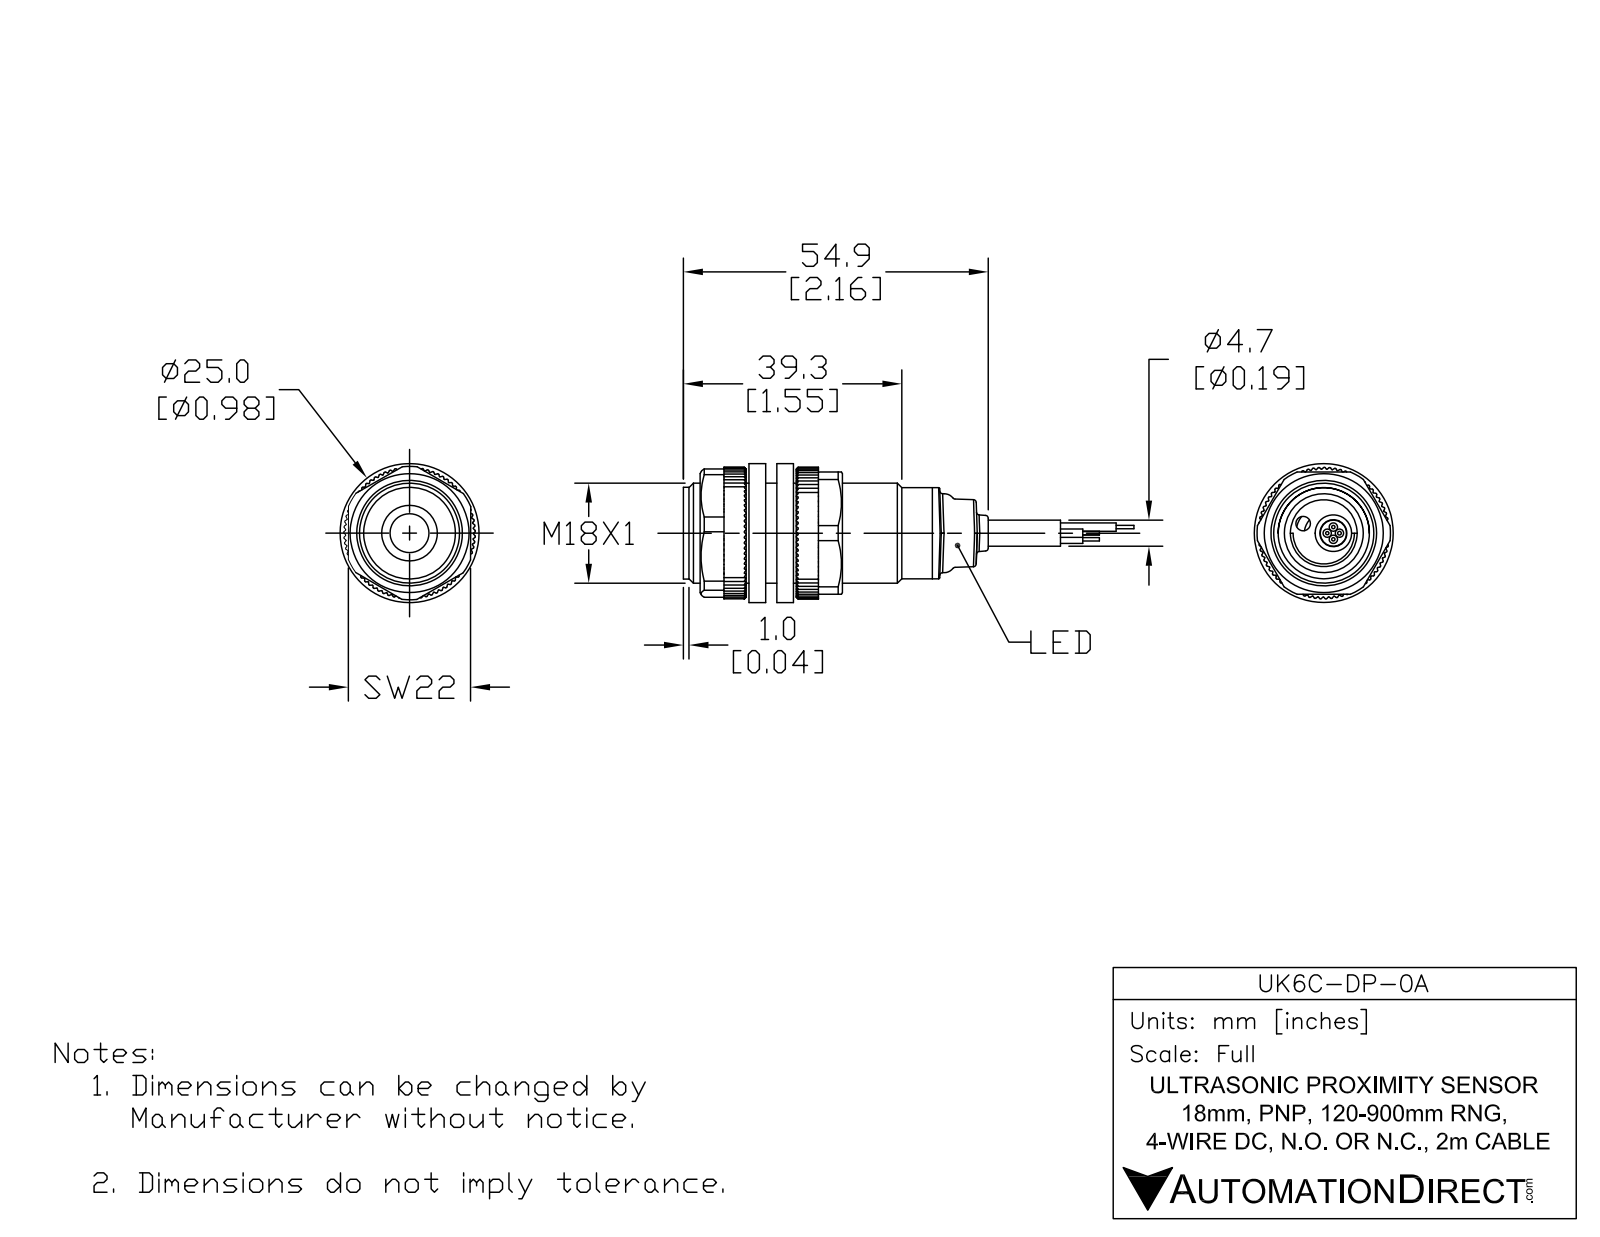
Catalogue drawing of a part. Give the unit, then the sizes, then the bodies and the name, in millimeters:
Units: millimetres
Overall size (bounding box): 89.8 × 18 × 18
Round holes (diameter × count): ⌀4.7 ×1, ⌀9.5 ×1
Round bosses / shafts (diameter × count): ⌀18 ×1, ⌀16.4 ×1, ⌀15.8 ×1, ⌀14.2 ×1
Partial cylindrical surfaces — rounded edges, fillets, slot ends (radius × count): R0.2 ×1, R0.5 ×1
Main face-to-face distances: 43.8, 1, 44.8, 1, 44.8, 49.9, 49.8, 48.8, 5.1, 6.5
Hole centre spacings: 1.7
Volume: 12 900 mm³ · Surface area: 4 795 mm²
Bodies: 4 solids, 62 faces (14 planar, 19 cylindrical, 29 other)
Part name (STEP PRODUCT): UK6C-DP-0A
STEP written by: SolidWorks 2017 (AUTOMOTIVE_DESIGN)
